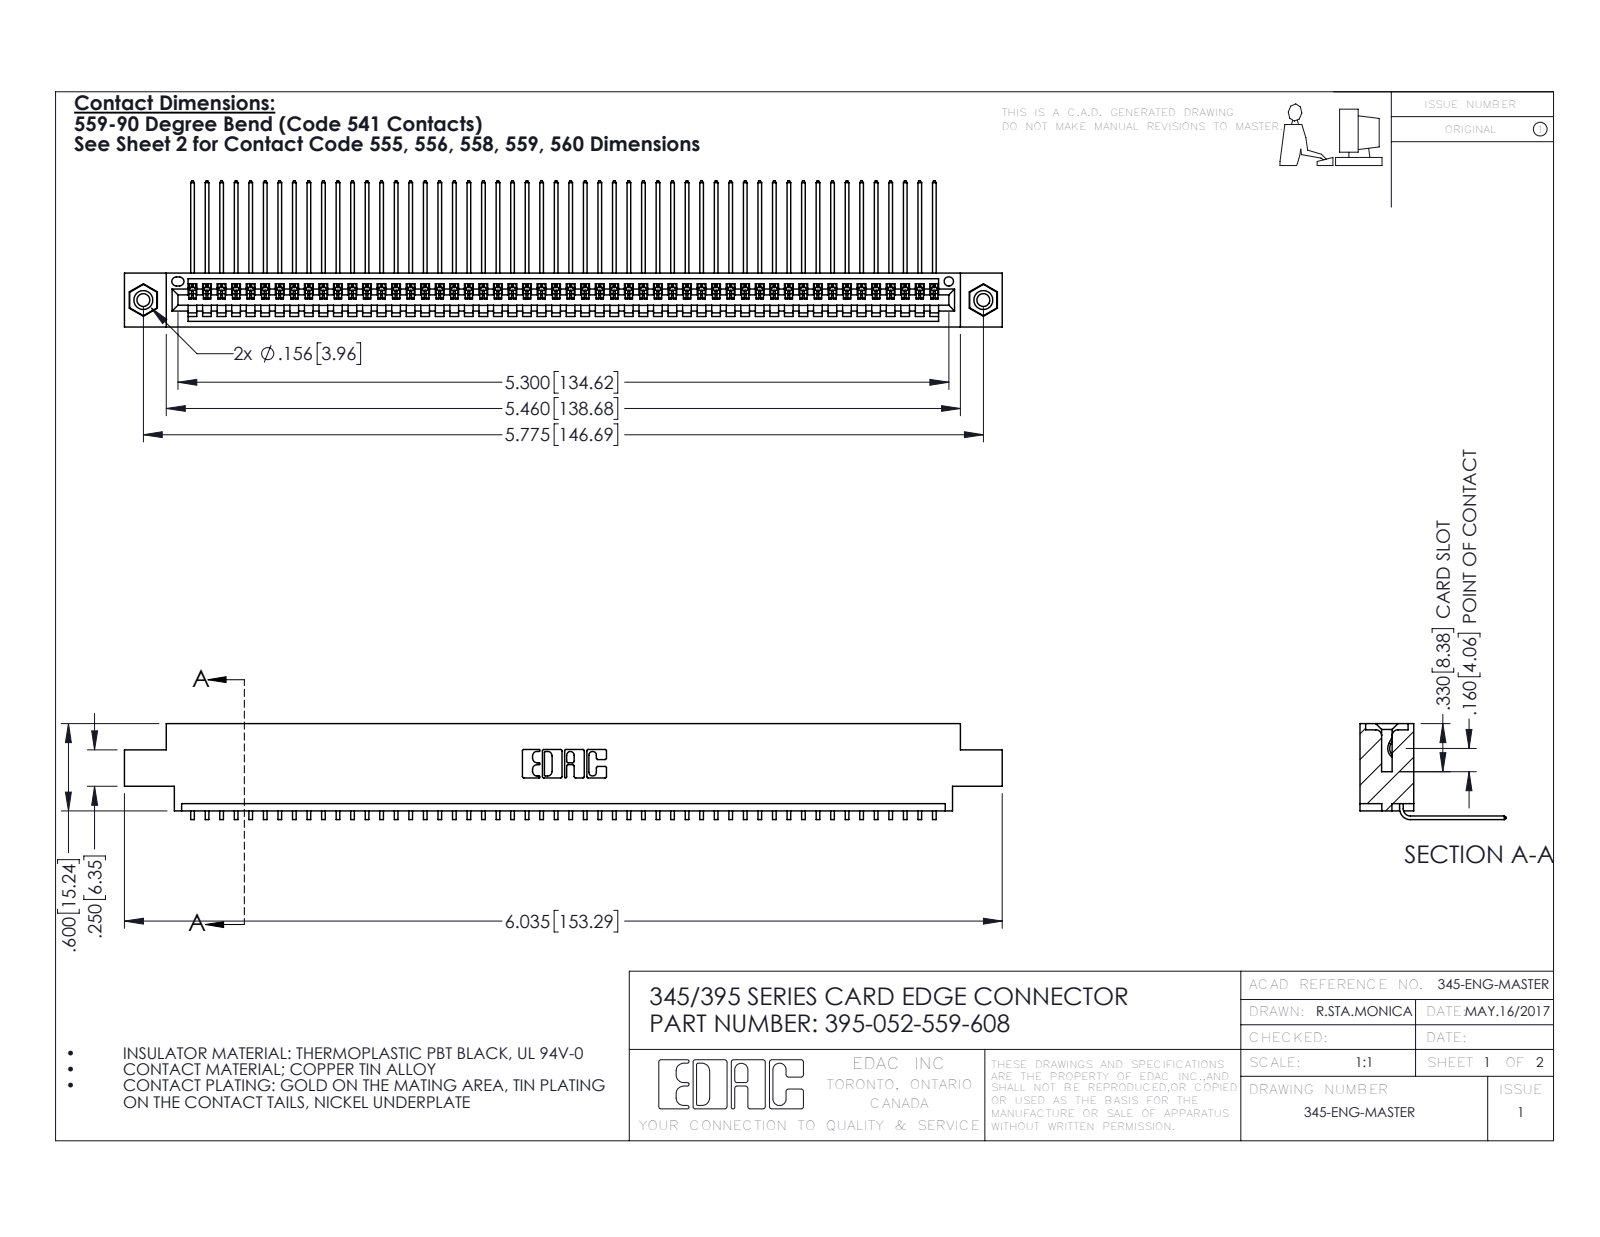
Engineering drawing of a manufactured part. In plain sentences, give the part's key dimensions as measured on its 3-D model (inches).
The part is named "345-292-001_558 559 Tail - 1; 395-052-559-608; 345 Part_0.170 Offset - 0.156 Dia-TI; 345-250-001_345-250-003-102". Its 3-D file was written by "SolidWorks 2016 (CONFIG_CONTROL_DESIGN)". It is 55 solids with 3310 faces: 2300 planar, 994 cylindrical and 16 other. Overall it measures 6.035 by 1.005 by 0.659 inches. Its volume is 0.897 cubic inches and its surface area 32.28 square inches. Round holes: 2 of diameter 0.089, 2 of diameter 0.125, 2 of diameter 0.156, 1 of diameter 0.064. Round bosses or shafts: 2 of diameter 0.155. Partial cylindrical surfaces (rounded edges, fillets, slot ends): 104 of radius 0.006, 22 of radius 0.01, 6 of radius 0.007, 6 of radius 0.031, 3 of radius 0.026, 2 of radius 0.031, 2 of radius 0.04, 1 of radius 0.014. The main face-to-face distances are 0.072, 0.298, 0.37, 0.2, 0.098, 0.272, 0.025, 0.225, 0.175, 0.149. The hole center spacings are 0.27, 5.539, 5.775.
